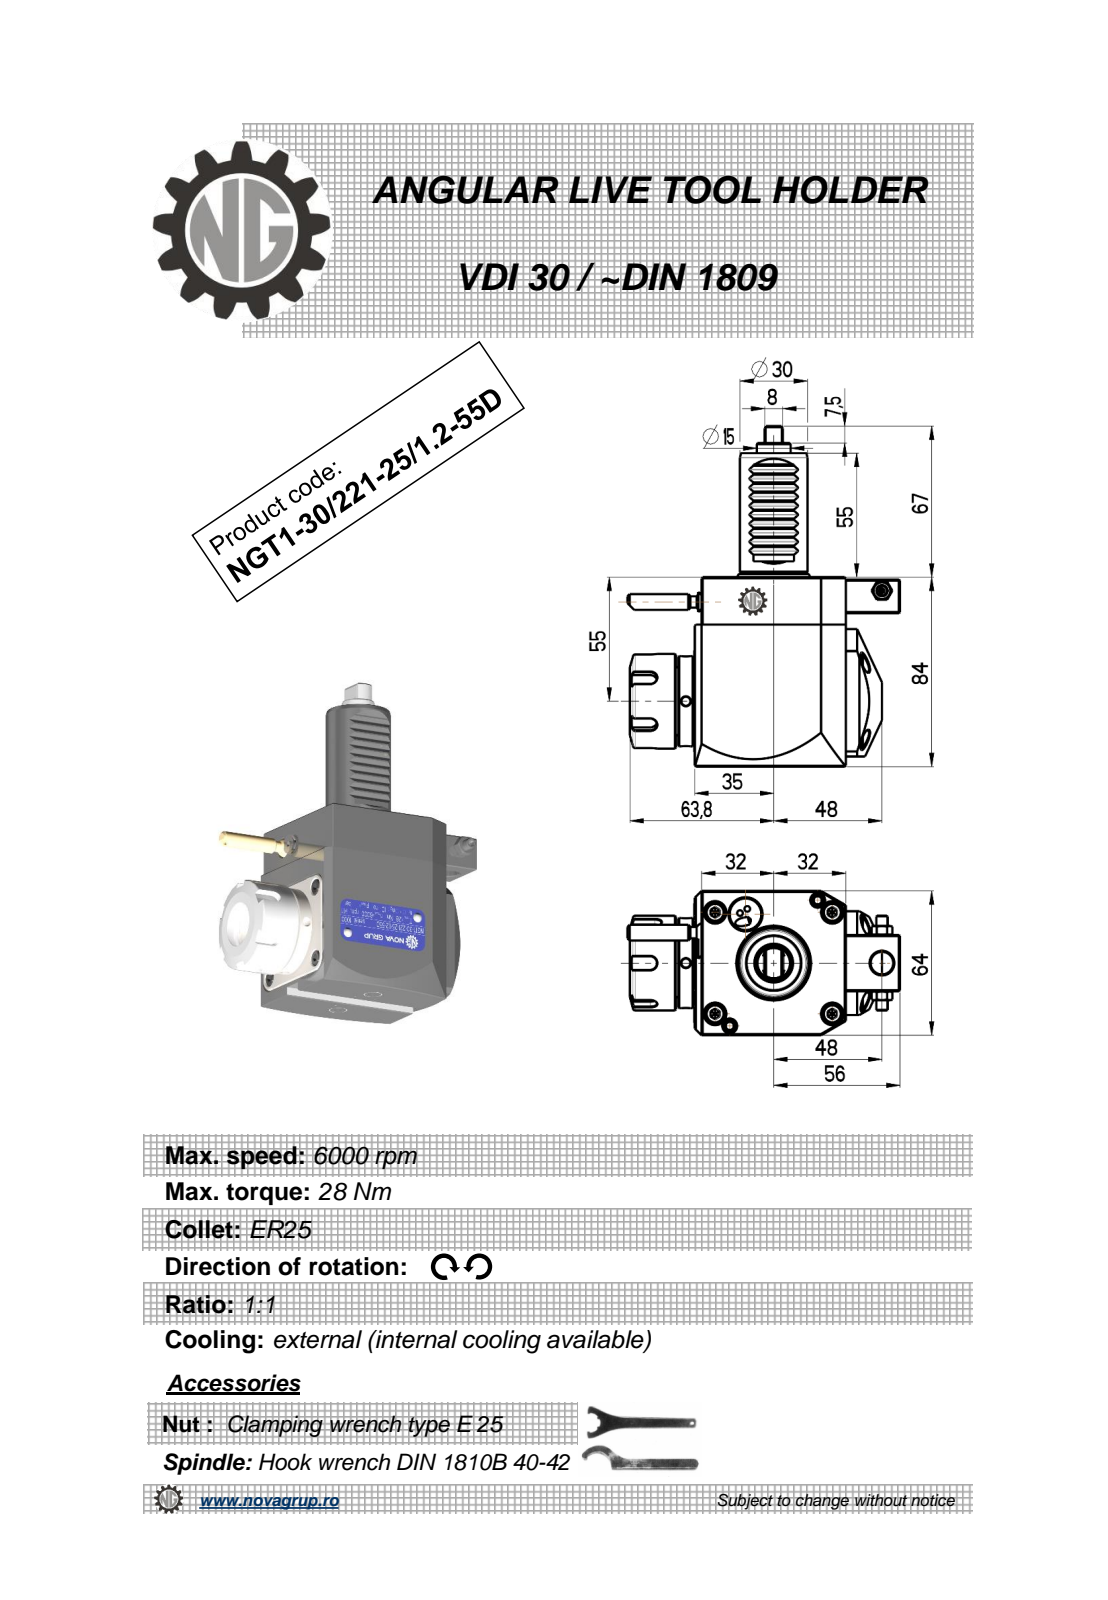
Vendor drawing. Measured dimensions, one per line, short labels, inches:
name: NGT1_30_221_25_1_2_55D
written by: PRO/ENGINEER BY PARAMETRIC TECHNOLOGY CORPORATION, 2010280 (CONFIG_CONTROL_DESIGN)
unit: in
bodies: 1 solid, 432 faces (194 planar, 92 cylindrical, 146 other)
size: 5.945 × 4.759 × 2.583
volume: 27.71 in³; area: 72.96 in²
holes: 2× ⌀0.157, 1× ⌀0.098, 1× ⌀0.118, 1× ⌀0.165, 1× ⌀0.374, 1× ⌀0.394, 1× ⌀0.799
bosses: 2× ⌀0.353, 2× ⌀0.197, 1× ⌀1.654, 1× ⌀1.575, 1× ⌀1.299, 1× ⌀1.181, 1× ⌀0.591, 1× ⌀0.276
rounds: 12× R0.01, 10× R0.012, 5× R0.118, 4× R0.138, 2× R0.031, 2× R6.299, 1× R0.283, 1× R1.26
face distances: 2.52, 3.307, 2.646, 2.638, 0.126, 0.118, 2.165, 3.268, 3.15, 0.02
hole spacings: 0.541, 1.812, 1.831, 3.423, 3.93
